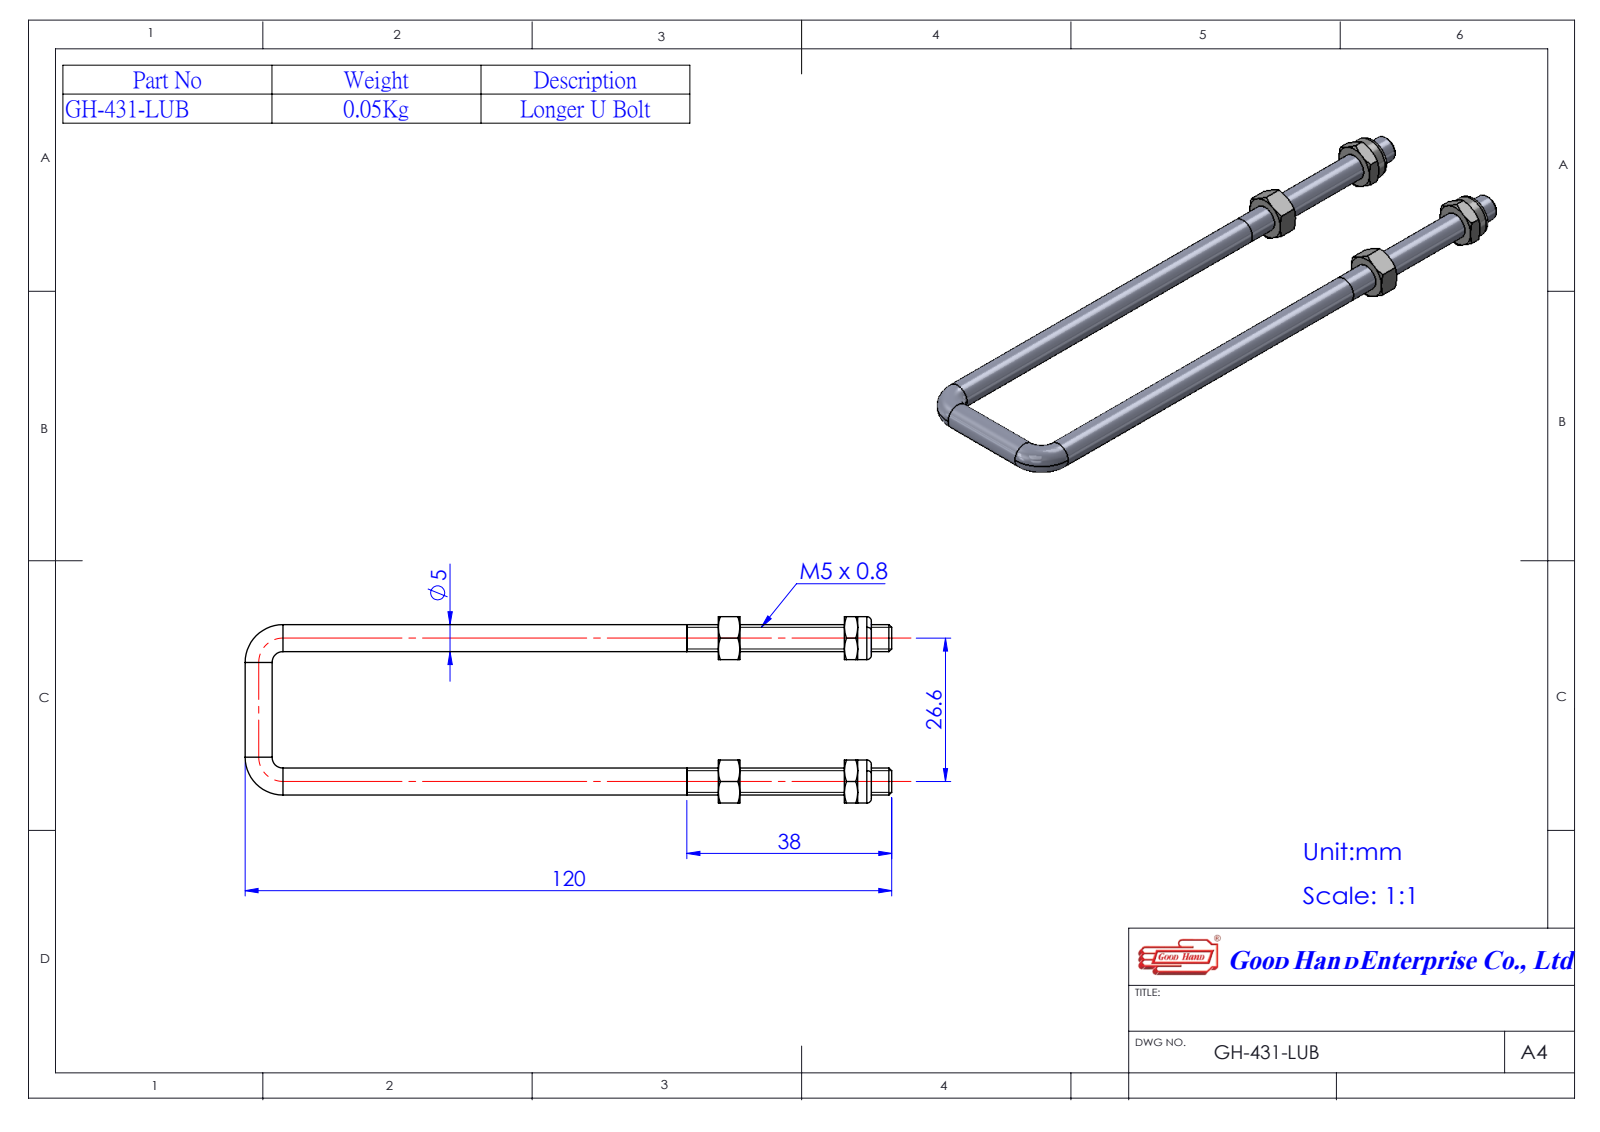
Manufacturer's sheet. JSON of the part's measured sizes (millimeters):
{"part_name": "443144; Hexagon Nut_2_JIS_JIS B 1181 Hexagon nut - Class 2 Finished M5 --N; prevailing torque nut thin insert_DIN_DIN EN ISO 10511 - M5 - N; GH-431-LUB", "step_written_by": "SolidWorks 2016 (AUTOMOTIVE_DESIGN)", "units": "millimeters", "bodies": {"solids": 7, "faces": 146, "planar": 40, "cylindrical": 34, "other": 72}, "overall_size": [120, 34.6, 9.24], "volume_mm3": 5739, "surface_area_mm2": 5167, "round_holes": [[4.2, 2], [5, 2], [5.86, 2]], "round_bosses_or_shafts": [[8, 2], [5, 1]], "face_to_face_distances": [8, 13.3, 29.25, 9.83, 19.42, 5.83, 4, 23.42, 21.3, 5.3], "hole_center_spacings": [26.6]}
